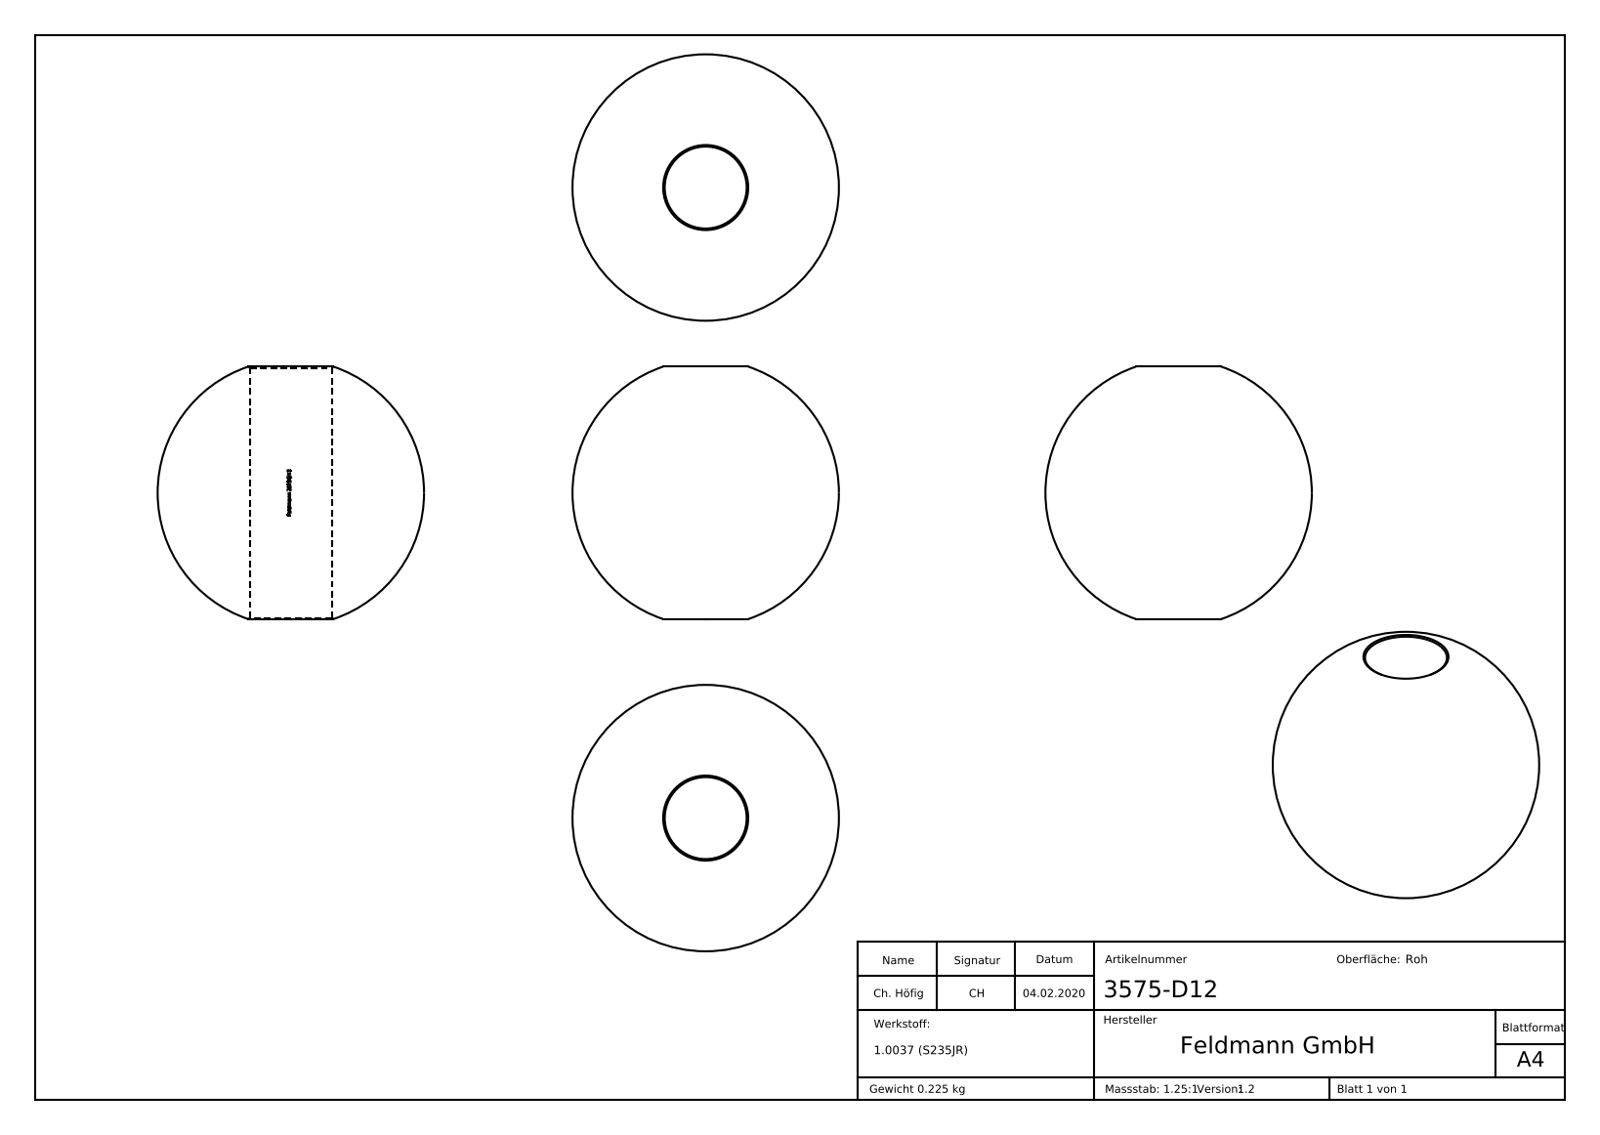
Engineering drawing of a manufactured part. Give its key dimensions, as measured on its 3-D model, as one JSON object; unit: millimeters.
{"part_name": "3575-D12", "step_written_by": "SolidWorks 2015 (CONFIG_CONTROL_DESIGN)", "units": "millimeters", "bodies": {"solids": 1, "faces": 212, "planar": 97, "cylindrical": 21, "other": 94}, "overall_size": [40, 40, 37.91], "volume_mm3": 28869, "surface_area_mm2": 6241, "round_holes": [[12.3, 1]], "partial_cylinders_radius": [[6.25, 1]], "face_to_face_distances": [4.83, 0.53, 0.5, 0.61, 0.45, 0.66, 2.54, 3.1, 1.18, 0.7]}
